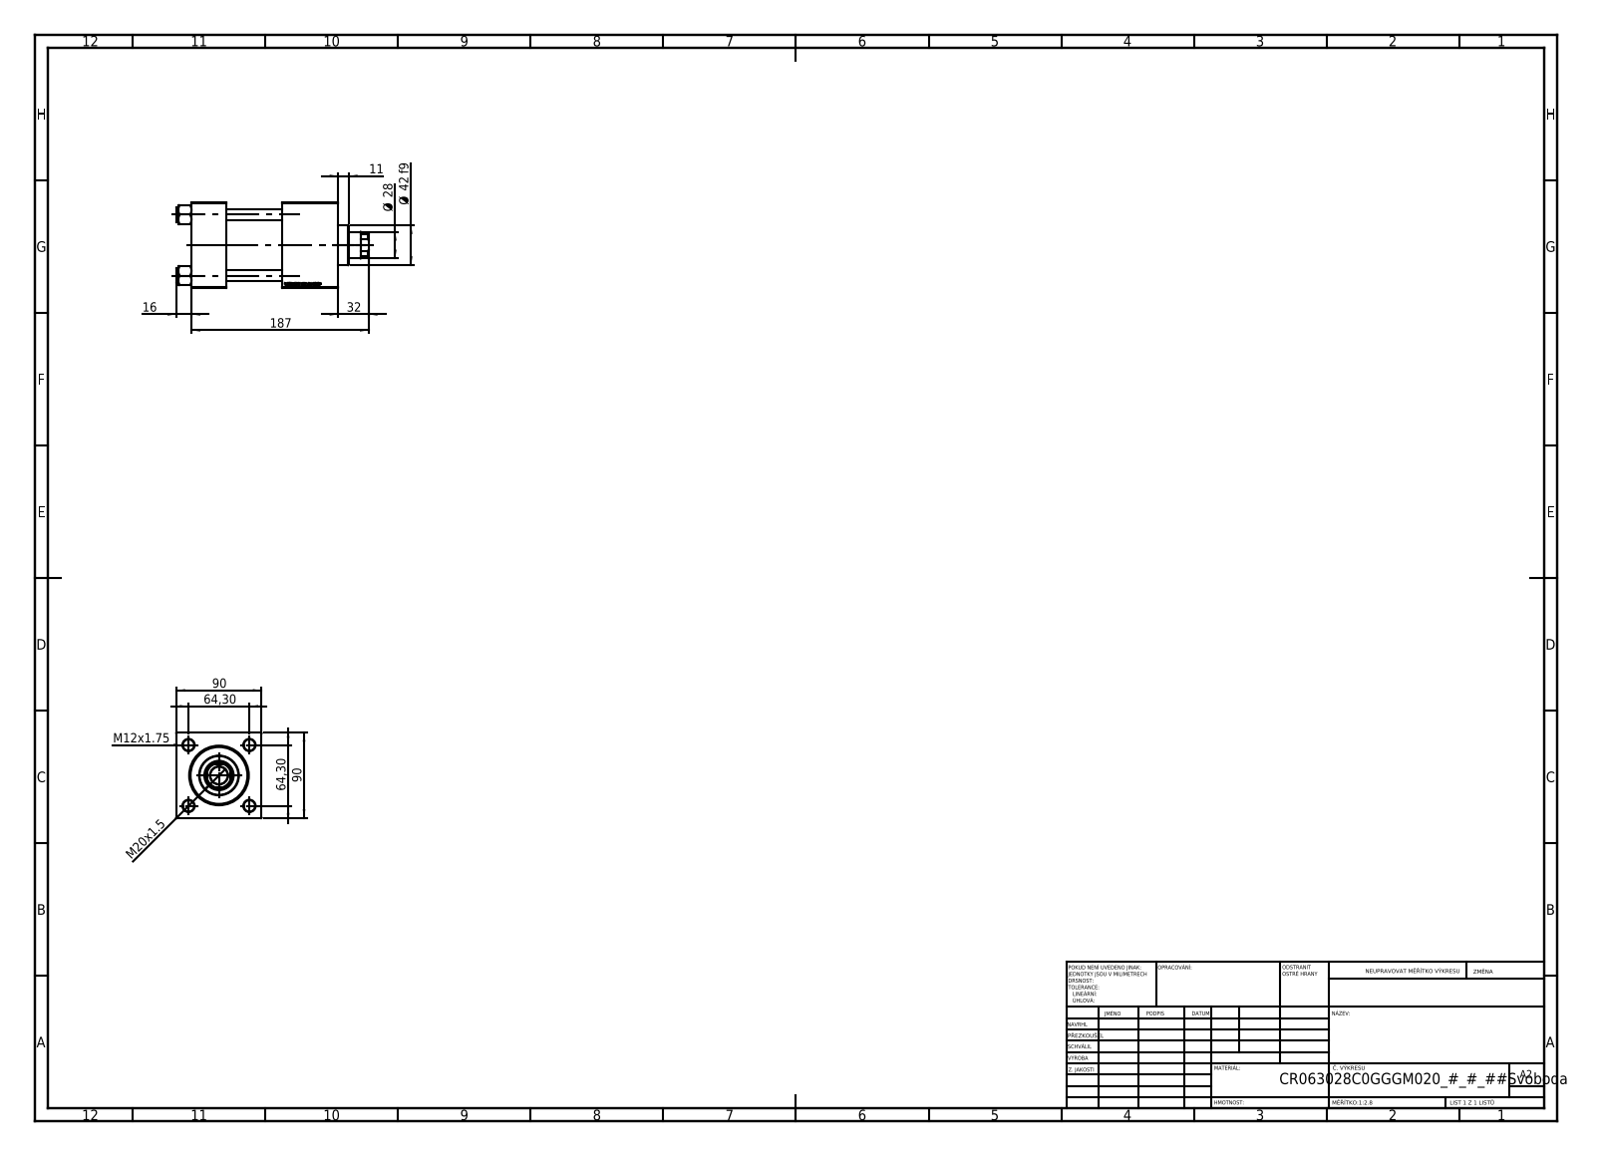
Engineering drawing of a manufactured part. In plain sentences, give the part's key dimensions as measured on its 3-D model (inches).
The part is named "V215_VC_A; V215CR_VCP_C; V215CR_C_Body; V215CR_C_TYCINKA (+1 more)". Its 3-D file was written by "SolidWorks 2019 (CONFIG_CONTROL_DESIGN)". It is 11 solids with 1149 faces: 526 planar, 87 cylindrical and 536 other. Overall it measures 7.992 by 3.543 by 3.543 inches. Its volume is 57.77 cubic inches and its surface area 277.7 square inches. Round holes: 4 of diameter 0.472, 2 of diameter 0.276, 2 of diameter 0.825, 2 of diameter 1.181, 1 of diameter 0.728, 1 of diameter 1.102, 1 of diameter 1.22, 1 of diameter 1.969, 1 of diameter 2.362, 1 of diameter 2.48. Round bosses or shafts: 4 of diameter 0.591, 1 of diameter 2.717, 1 of diameter 1.654. Partial cylindrical surfaces (rounded edges, fillets, slot ends): 1 of radius 0.531. The main face-to-face distances are 3.543, 2.323, 1.457, 6.102, 4.646, 3.78, 4.972, 3.516, 1.193, 1.13. The hole center spacings are 1.79, 2.531, 3.58, 3.839.
